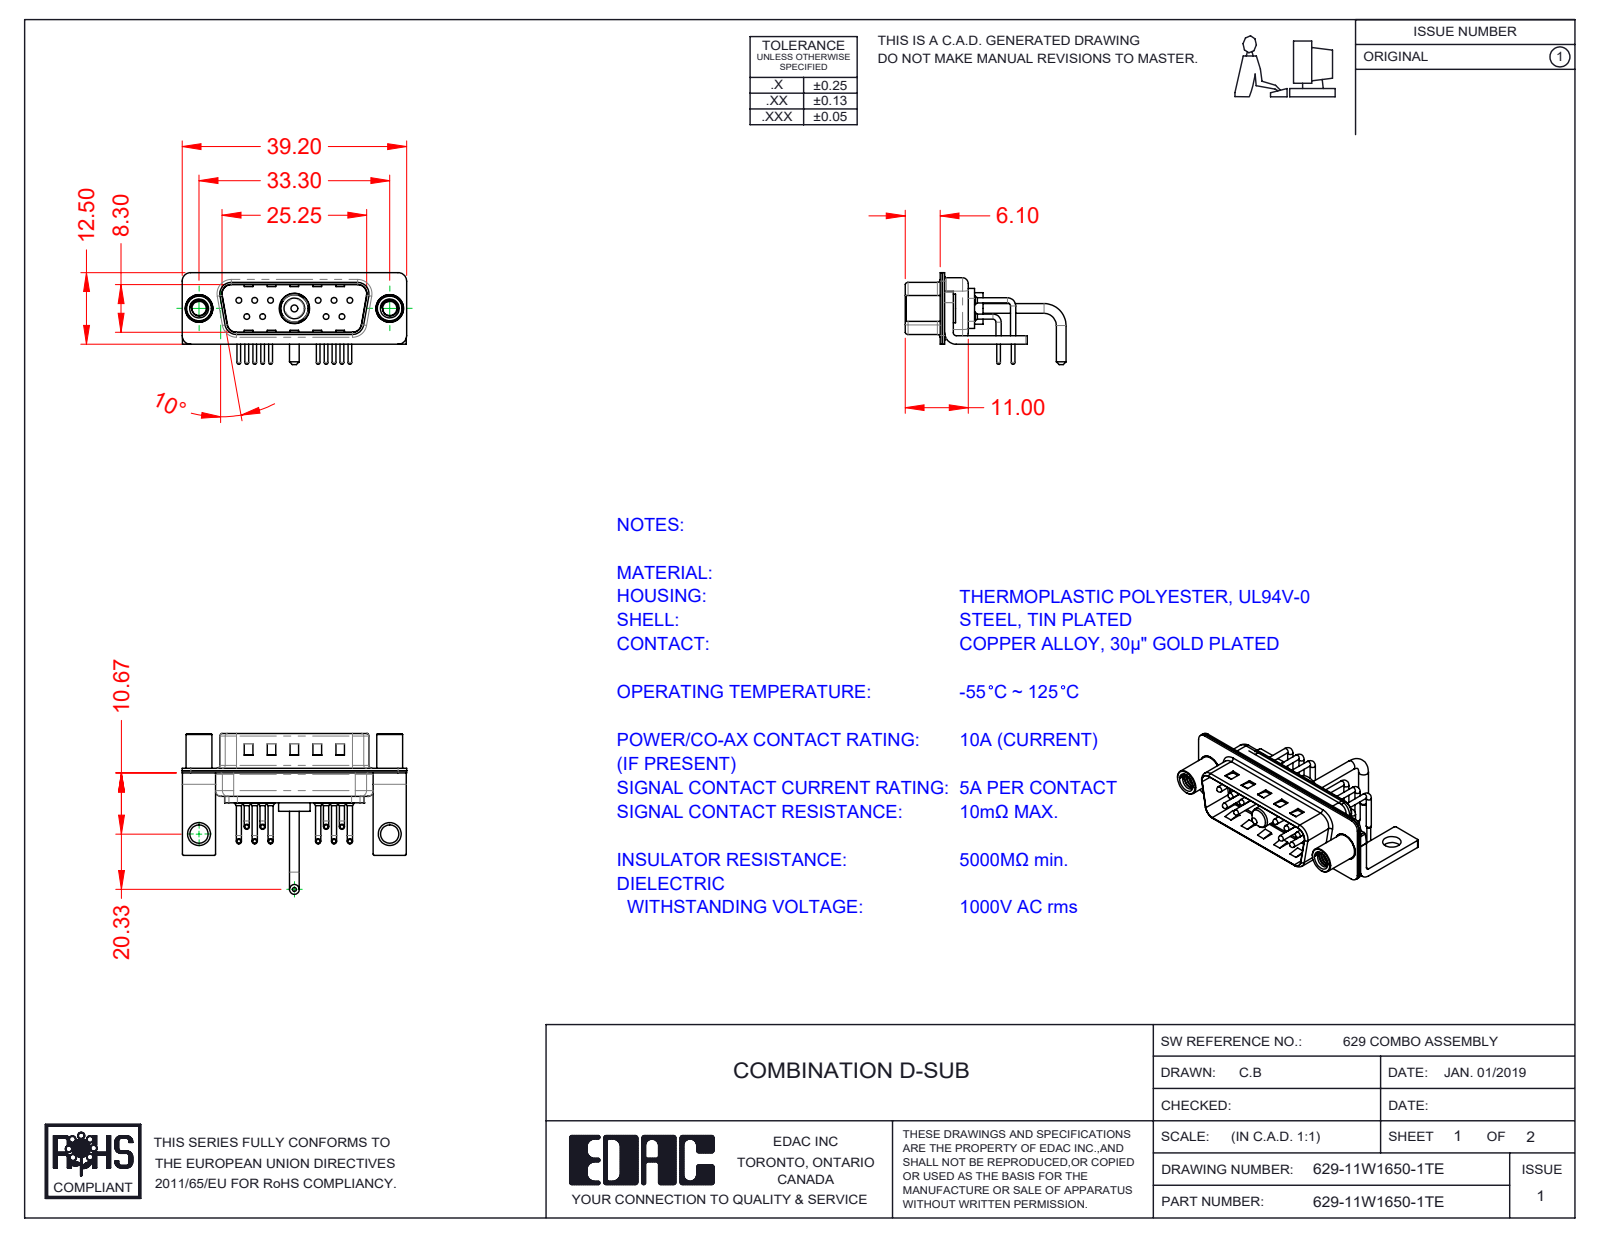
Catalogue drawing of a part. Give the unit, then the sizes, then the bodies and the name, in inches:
Units: inches
Overall size (bounding box): 1.543 × 1.106 × 0.632
Round holes (diameter × count): ⌀0.03 ×10, ⌀0.063 ×10, ⌀0.079 ×10, ⌀0.098 ×2, ⌀0.126 ×2, ⌀0.157 ×2, ⌀0.189 ×2, ⌀0.191 ×1, ⌀0.209 ×1
Round bosses / shafts (diameter × count): ⌀0.035 ×20, ⌀0.059 ×10, ⌀0.039 ×10, ⌀0.026 ×10, ⌀0.197 ×2, ⌀0.193 ×2, ⌀0.177 ×2, ⌀0.067 ×2
Partial cylindrical surfaces — rounded edges, fillets, slot ends (radius × count): R0.01 ×16, R0.059 ×16, R0.079 ×13, R0.04 ×10, R0.02 ×9, R0.063 ×8, R0.039 ×7, R0.024 ×4
Main face-to-face distances: 0.016, 0.031, 0.059, 0.374, 0.358, 0.343, 0.39, 0.024, 0.075, 0.205
Hole centre spacings: 0.124, 0.109, 0.545, 0.436, 0.654, 0.198, 0.198, 0.218
Volume: 0.147 in³ · Surface area: 9.525 in²
Bodies: 19 solids, 1594 faces (820 planar, 590 cylindrical, 184 other)
Part name (STEP PRODUCT): 629Combo Contact Row 2; 629Combo Contact Row 1; Power Pin_Ext 10A RA; 629Combo Threaded Standoff_D (+5 more)
STEP written by: SolidWorks 2020 (CONFIG_CONTROL_DESIGN)
